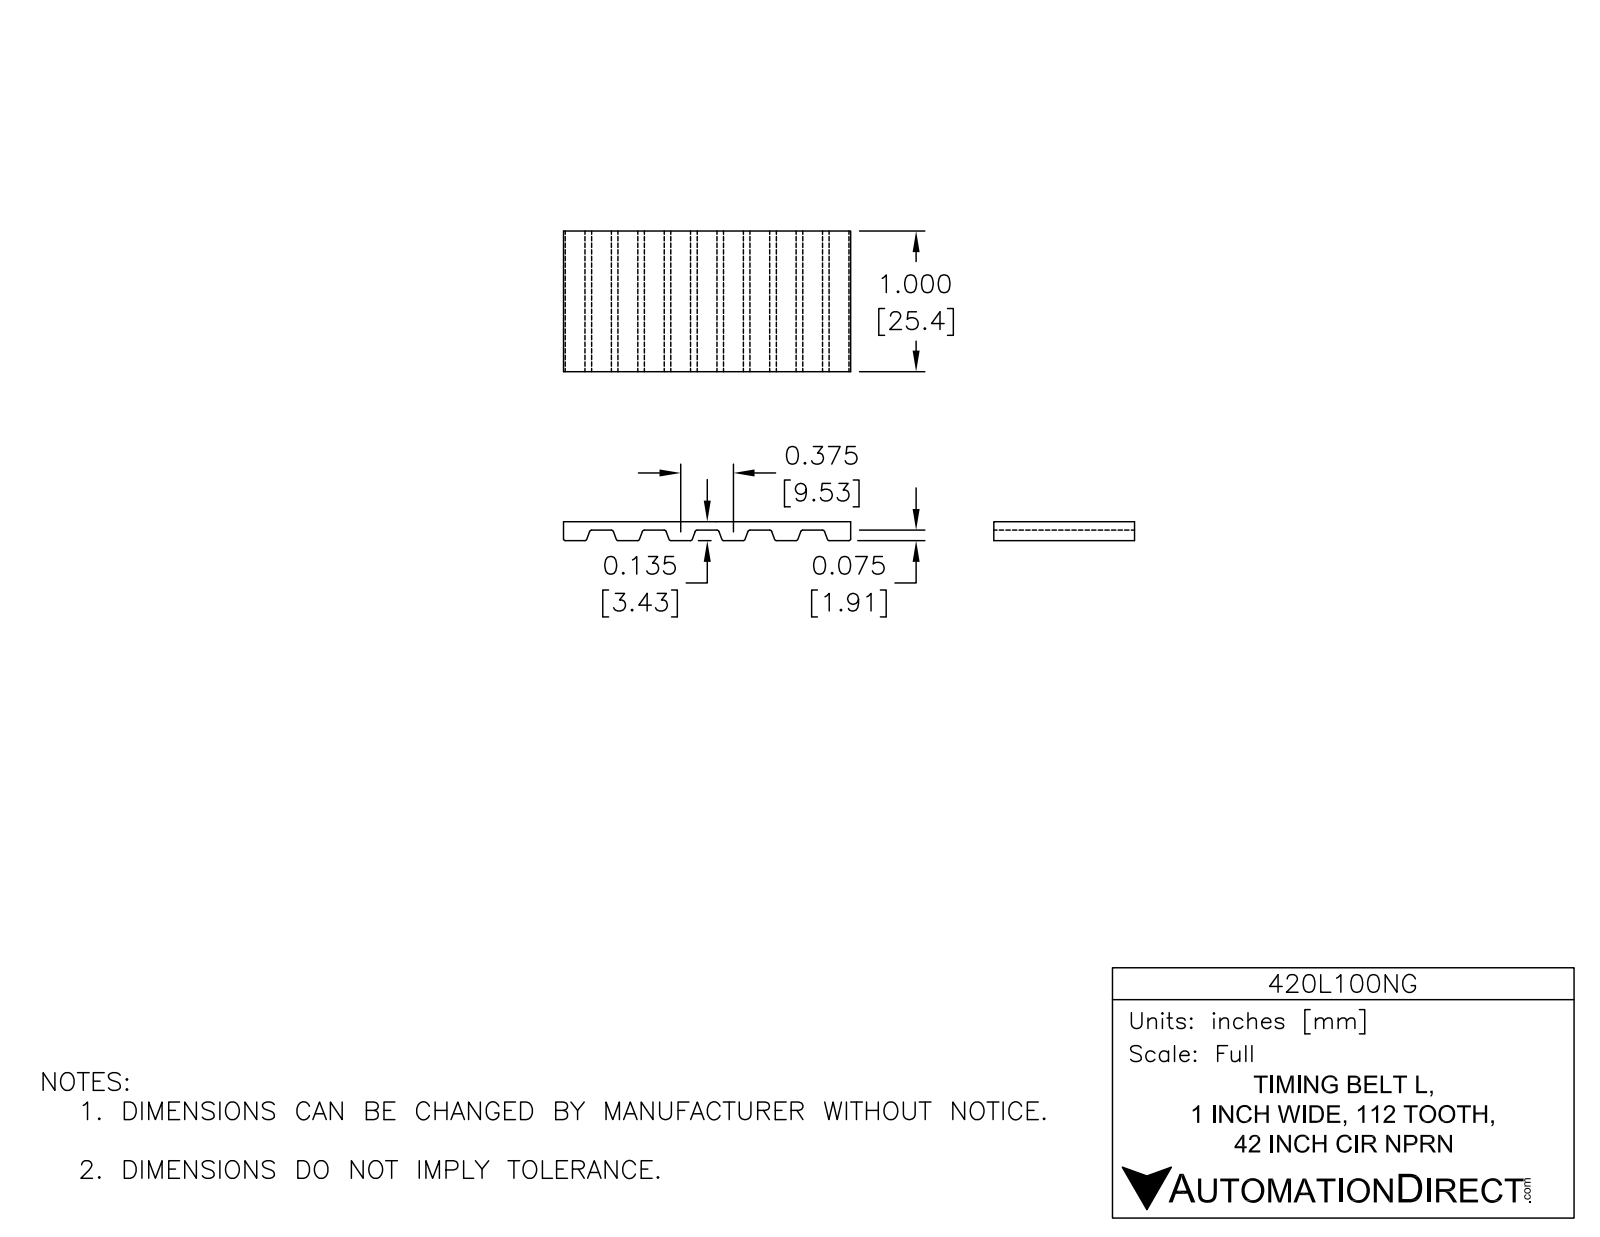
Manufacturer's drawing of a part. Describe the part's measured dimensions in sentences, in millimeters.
The part is named "420L100NG". Its 3-D file was written by "SolidWorks 2014 (AUTOMOTIVE_DESIGN)". It is 1 solid with 912 faces: 425 planar, 487 cylindrical and 0 other. Overall it measures 489.9 by 76.2 by 25.4 millimeters. Its volume is 62 420 cubic millimeters and its surface area 65 350 square millimeters. Partial cylindrical surfaces (rounded edges, fillets, slot ends): 444 of radius 0.5, 2 of radius 36.4, 2 of radius 38.1. The main face-to-face distances are 1.7, 74.5, 76.2, 72.9, 3.6, 72.6, 1.9, 71, 25.4, 69.1.
